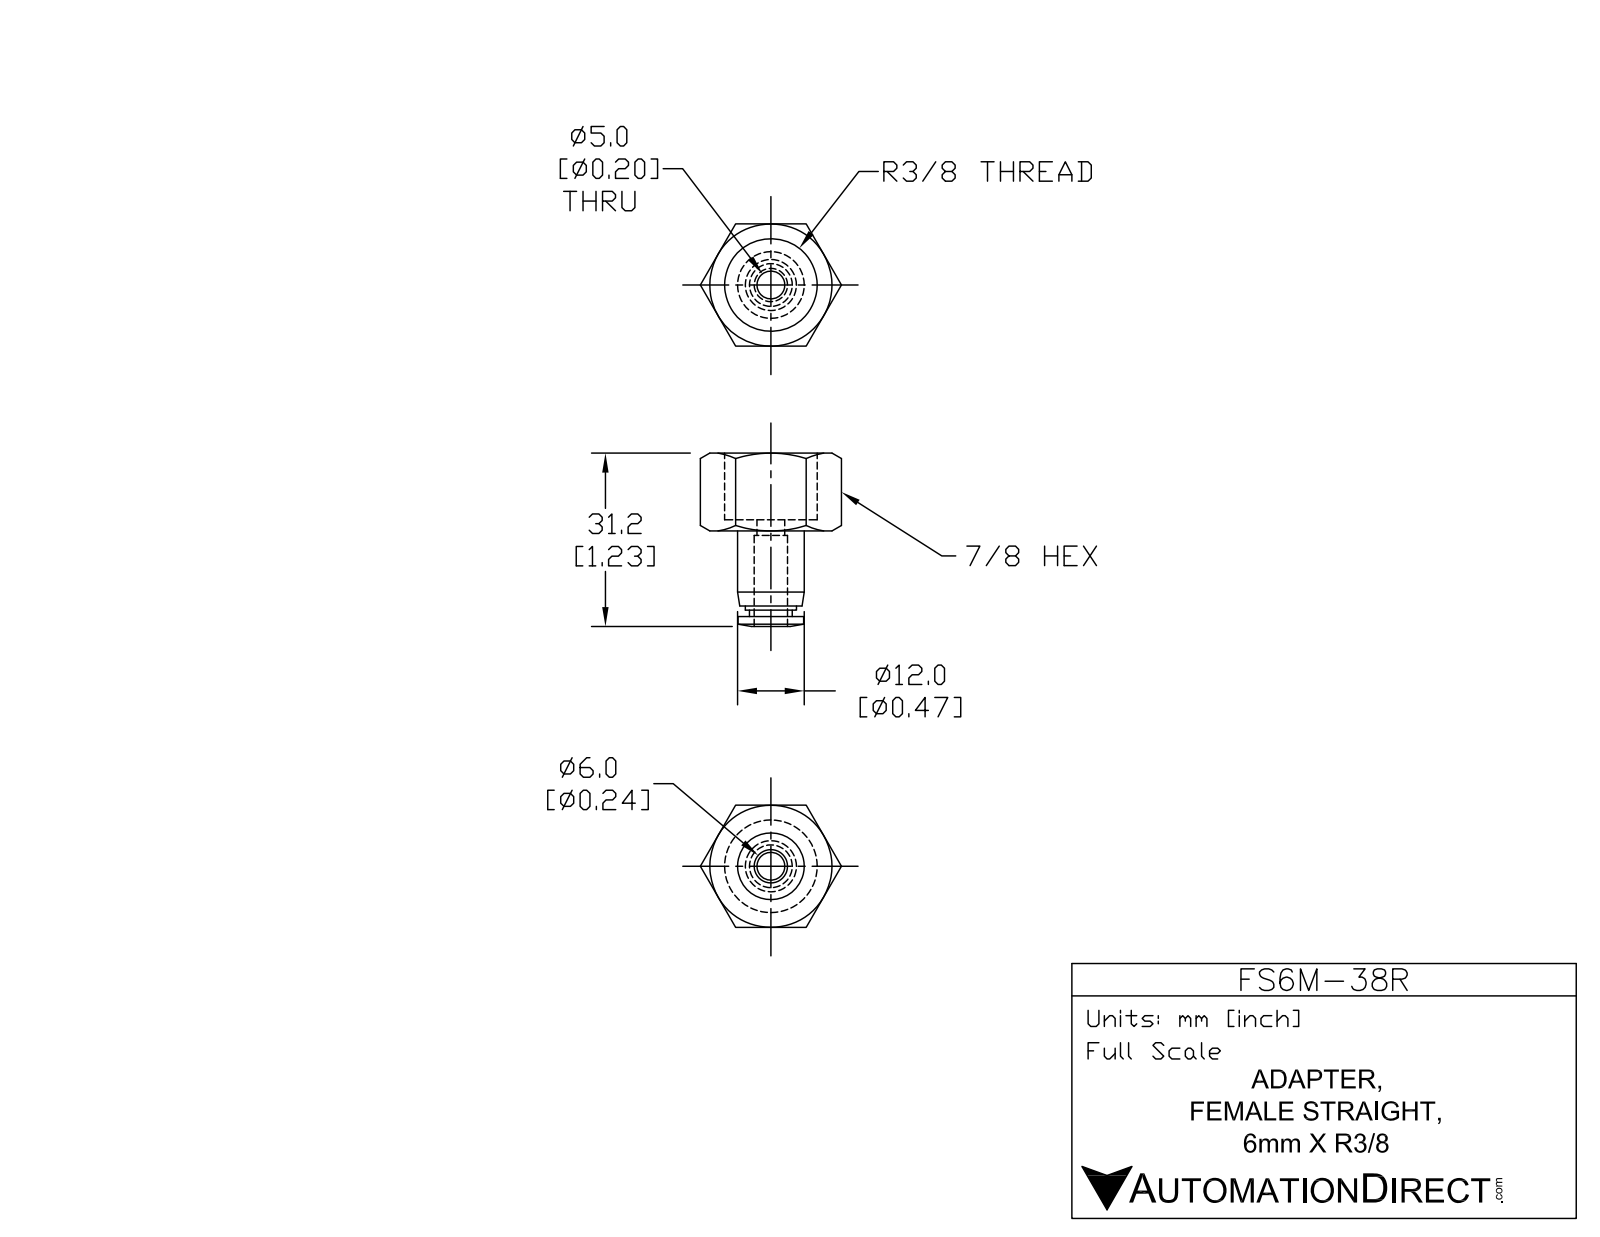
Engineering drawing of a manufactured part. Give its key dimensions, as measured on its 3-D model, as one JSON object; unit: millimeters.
{"part_name": "FS6M-38R", "step_written_by": "SolidWorks 2015 (AUTOMOTIVE_DESIGN)", "units": "millimeters", "bodies": {"solids": 1, "faces": 46, "planar": 14, "cylindrical": 12, "other": 20}, "overall_size": [31.2, 25.4, 22], "volume_mm3": 4570, "surface_area_mm2": 3508, "round_holes": [[5, 1], [6.3, 1]], "round_bosses_or_shafts": [[12, 1], [11.8, 1], [9.2, 1], [7.7, 1]], "face_to_face_distances": [22, 2, 12, 14, 29.4, 17.4, 15.4, 27.5, 15.5, 13.5]}
